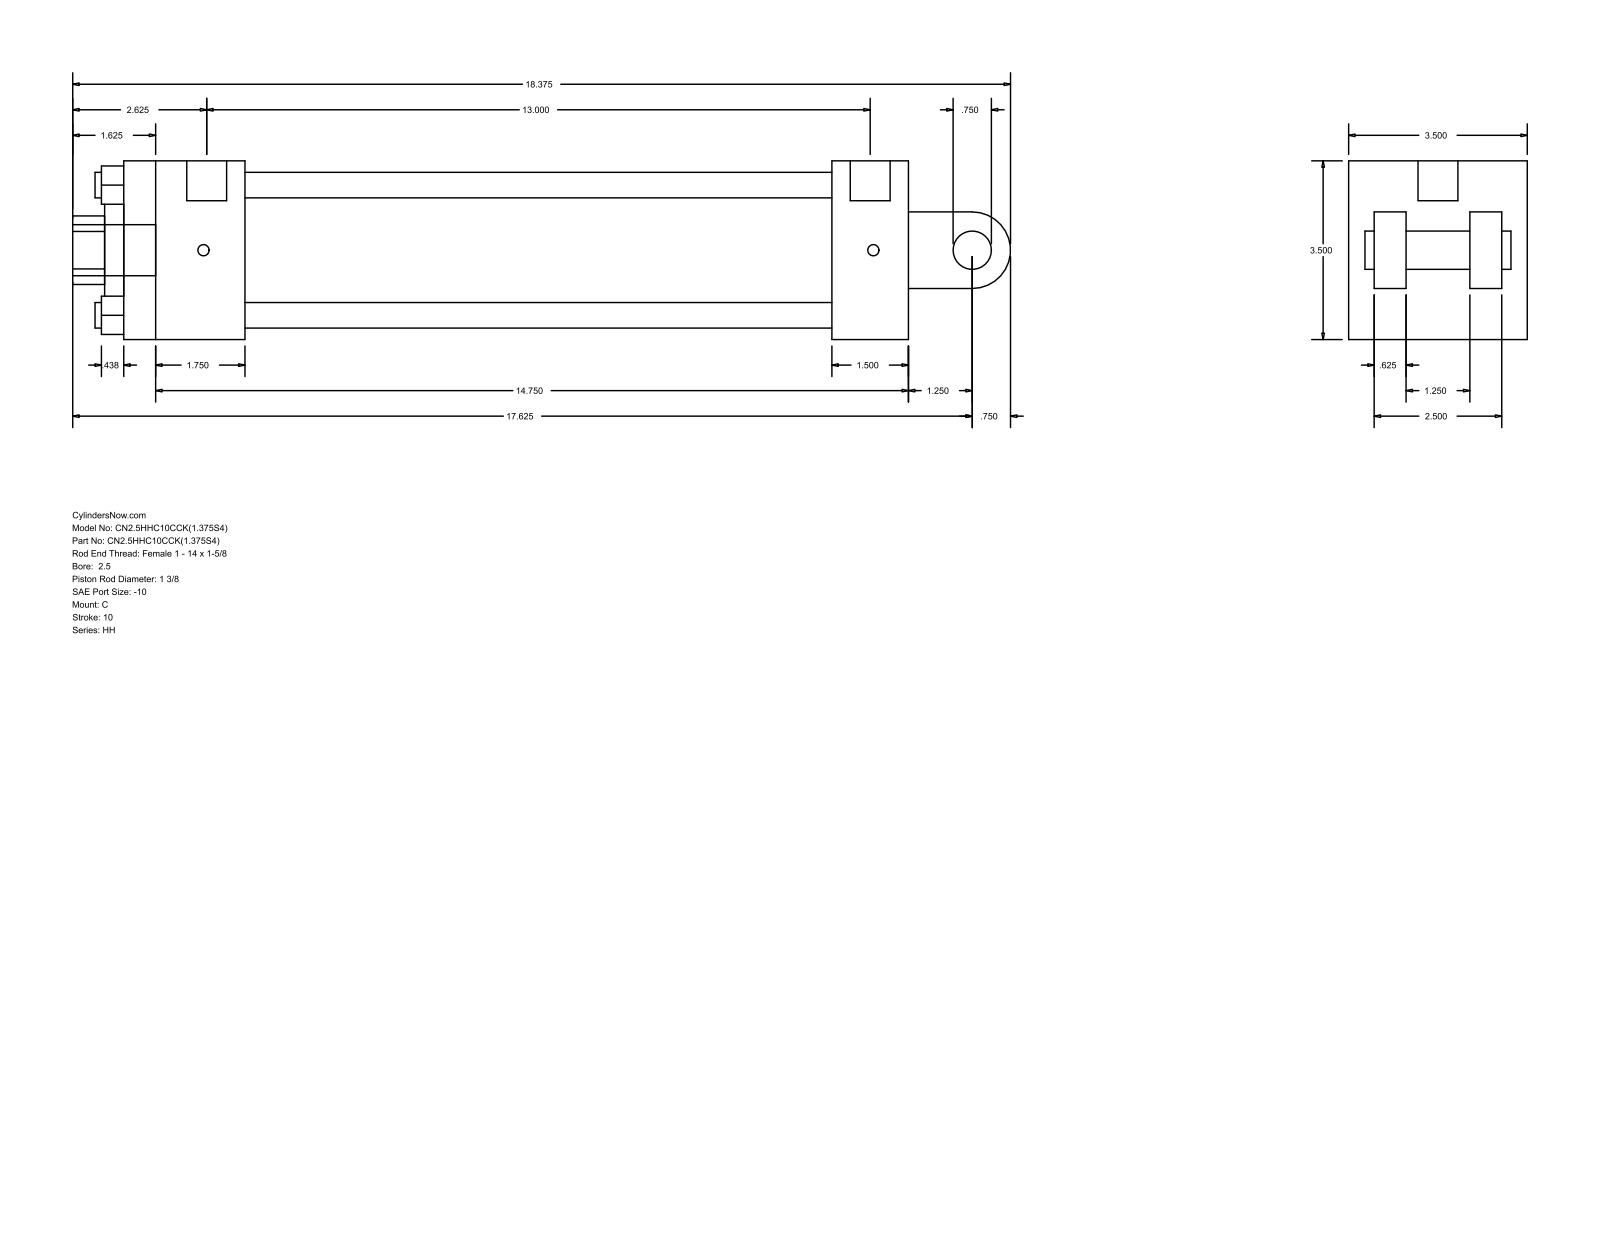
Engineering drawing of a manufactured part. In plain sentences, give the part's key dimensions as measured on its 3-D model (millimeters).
The part is named "HH_C__0250_1.375". Its 3-D file was written by "GSSL Pune (CONFIG_CONTROL_DESIGN)". It is 0 solids with 99 faces: 70 planar, 29 cylindrical and 0 other. Overall it measures 466.73 by 88.9 by 88.9 millimeters. Round holes: 4 of diameter 12.7, 2 of diameter 5.56, 1 of diameter 19.84, 1 of diameter 34.92, 1 of diameter 50.8, 1 of diameter 73.03. Round bosses or shafts: 2 of diameter 5.56, 1 of diameter 25.4, 1 of diameter 19.84, 1 of diameter 19.05. Partial cylindrical surfaces (rounded edges, fillets, slot ends): 1 of radius 17.06, 1 of radius 19.05. The main face-to-face distances are 88.9, 390.53, 63.5, 15.87, 12.7, 352.42, 38.11, 60.32, 292.1, 330.21. The hole center spacings are 45.79, 64.76, 91.58, 1.58.
